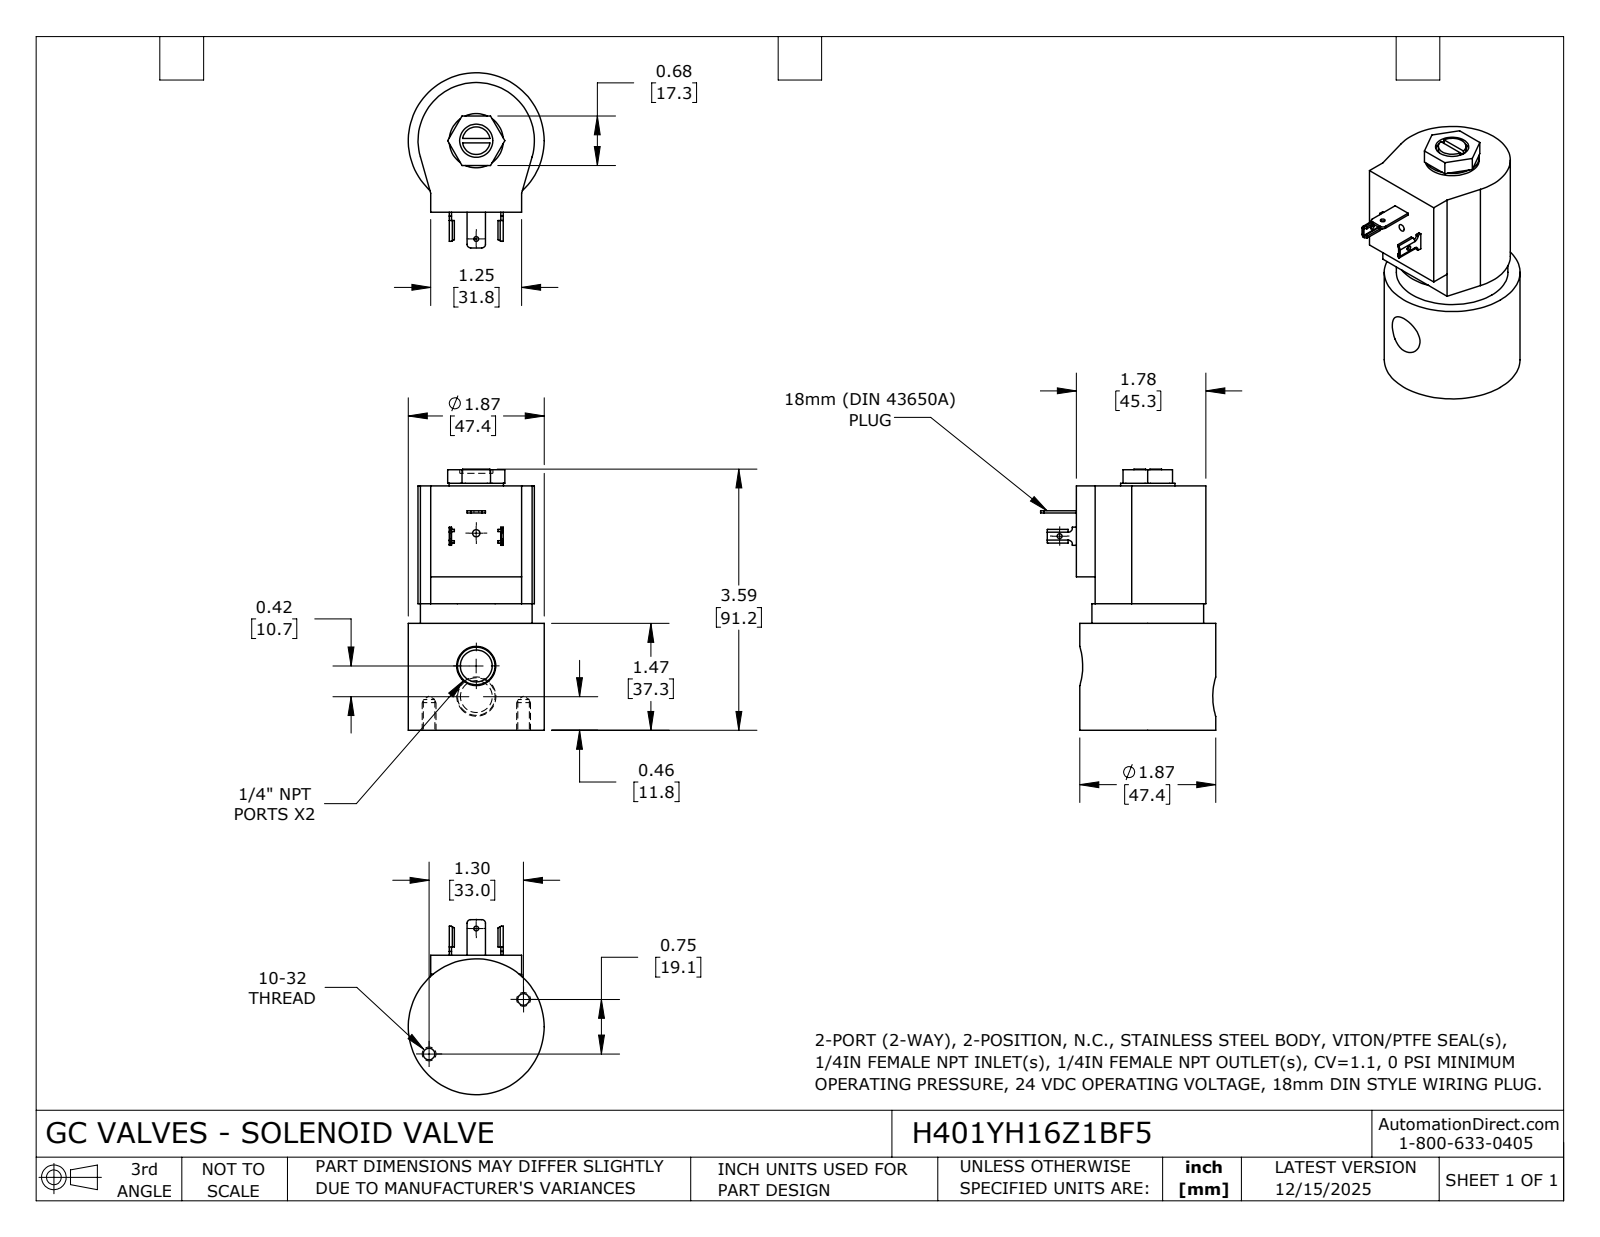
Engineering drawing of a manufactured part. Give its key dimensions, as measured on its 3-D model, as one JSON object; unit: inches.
{"part_name": "H401YH16Z1BF5", "step_written_by": "SolidWorks 2024 (CONFIG_CONTROL_DESIGN)", "units": "inches", "bodies": {"solids": 1, "faces": 132, "planar": 75, "cylindrical": 43, "other": 14}, "overall_size": [3.591, 2.407, 1.868], "volume_in3": 8.118, "surface_area_in2": 29.18, "round_holes": [[0.159, 2], [0.438, 2], [0.066, 1], [0.067, 1], [0.1, 1], [0.456, 1]], "round_bosses_or_shafts": [[1.868, 1], [1.535, 1], [0.746, 1], [0.38, 1]], "partial_cylinders_radius": [[0.006, 4], [0.041, 4], [0.05, 2], [0.06, 2], [0.8, 1]], "face_to_face_distances": [3.36, 1.47, 1.89, 0.26, 2.11, 0.64, 1.25, 1.25, 3.583, 2.113], "hole_center_spacings": [0.75, 0.422, 1.171, 1.35, 1.5, 1.824, 1.843, 2.246]}
